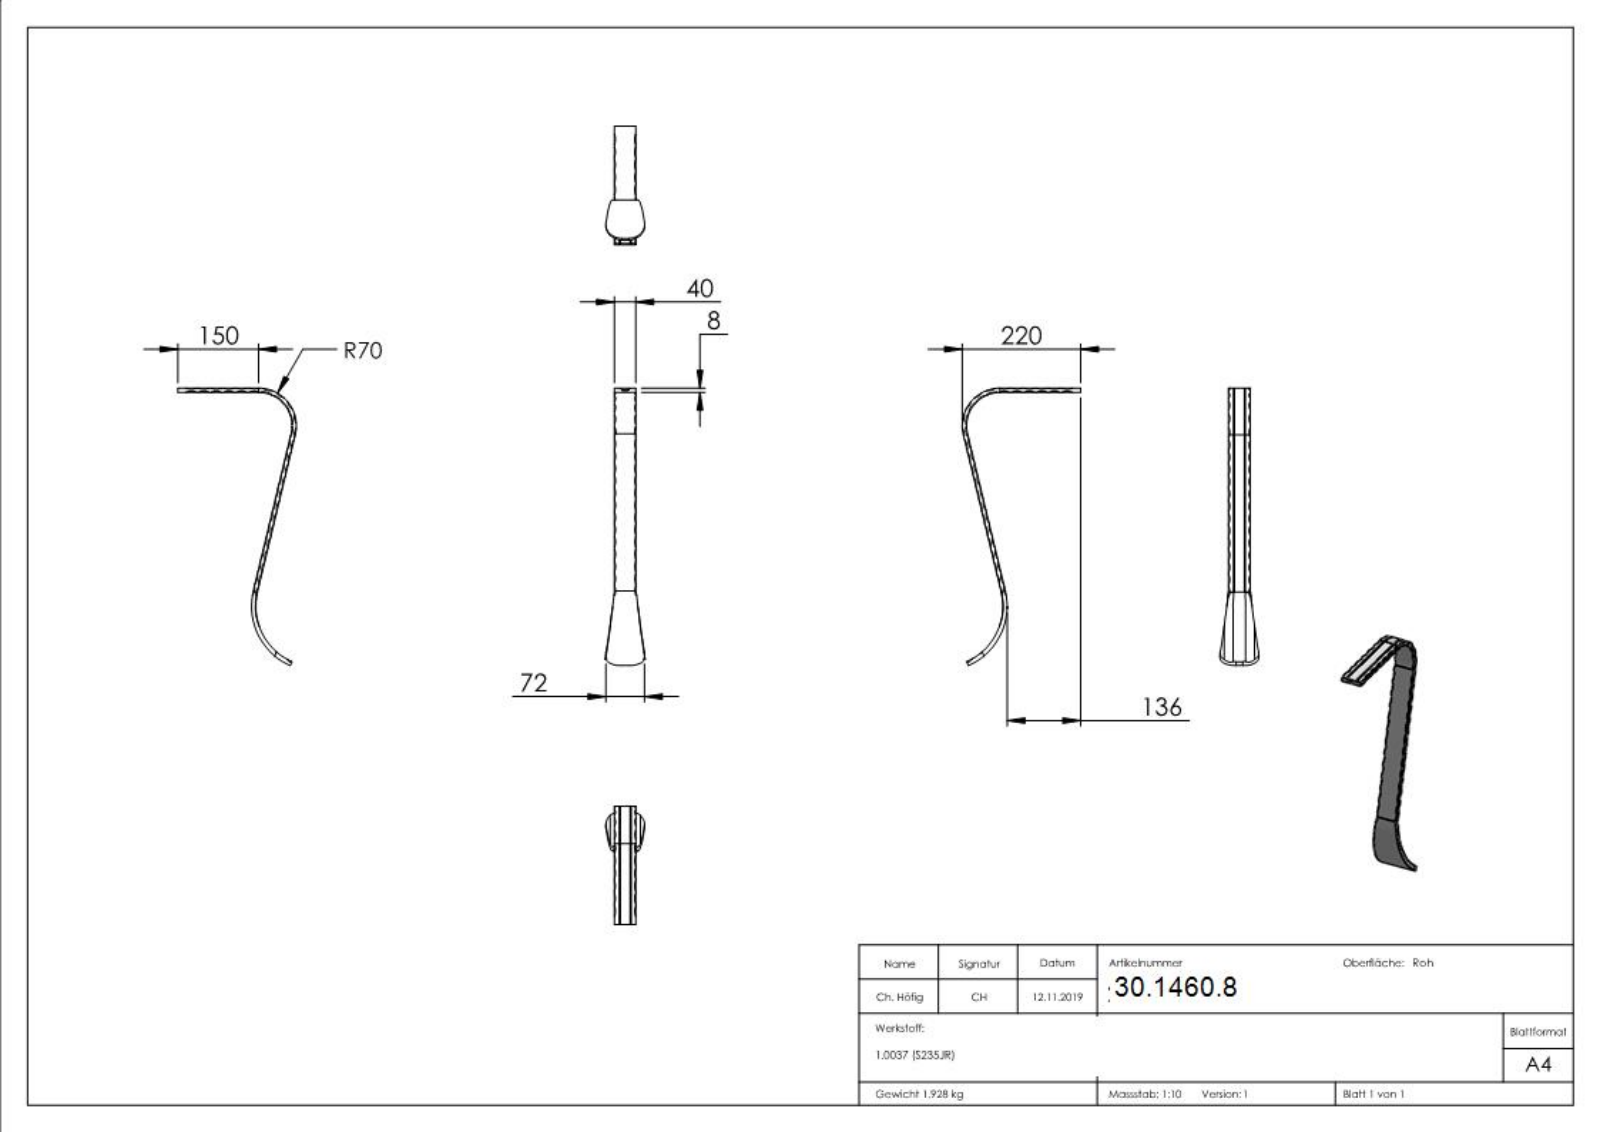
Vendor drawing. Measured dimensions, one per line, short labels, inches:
name: 2071
written by: SolidWorks 2015 (CONFIG_CONTROL_DESIGN)
unit: in
bodies: 1 solid, 291 faces (114 planar, 4 cylindrical, 173 other)
size: 20.276 × 8.661 × 2.85
volume: 15.08 in³; area: 118 in²
rounds: 1× R2.441, 1× R2.756
face distances: 0.315, 1.575, 0.557, 4.369, 0.157, 0.015, 0.117, 0.052, 0.502, 0.373
